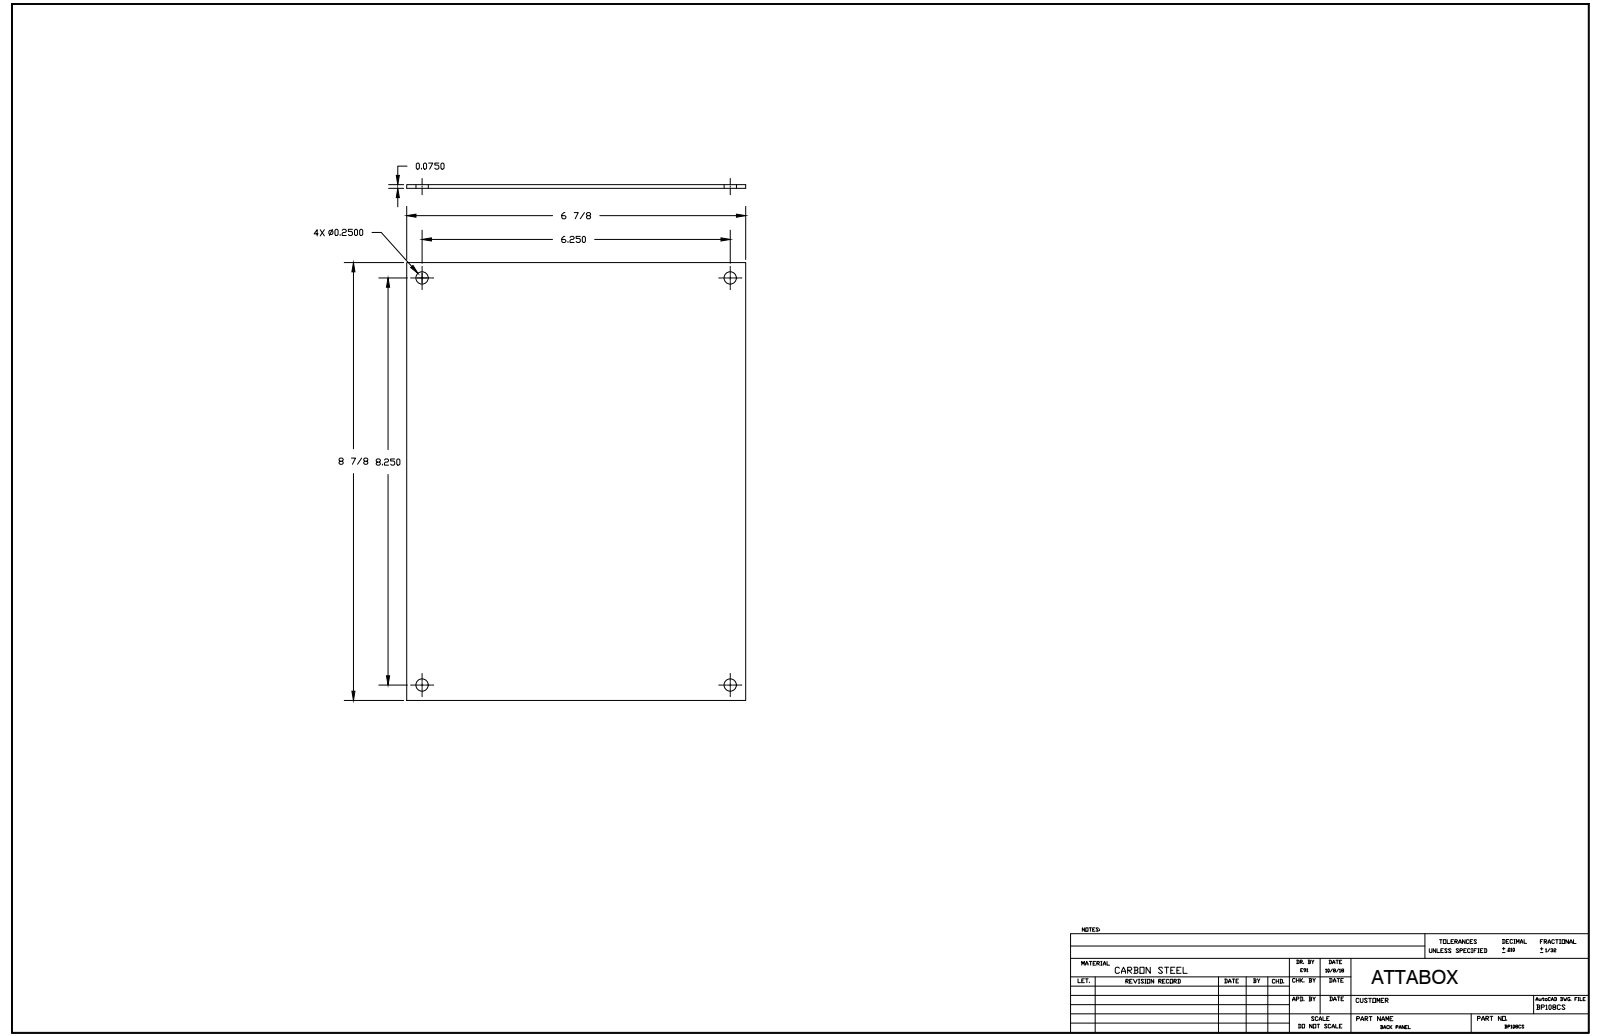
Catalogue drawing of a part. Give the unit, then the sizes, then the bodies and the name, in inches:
Units: inches
Overall size (bounding box): 8.875 × 6.875 × 0.075
Round holes (diameter × count): ⌀0.25 ×4
Main face-to-face distances: 0.075, 6.875, 8.875
Hole centre spacings: 6.25, 8.25, 10.35
Volume: 4.561 in³ · Surface area: 124.2 in²
Bodies: 1 solid, 10 faces (6 planar, 4 cylindrical, 0 other)
Part name (STEP PRODUCT): BP108CS_STP
STEP written by: Autodesk Inventor 2014 (AUTOMOTIVE_DESIGN)
